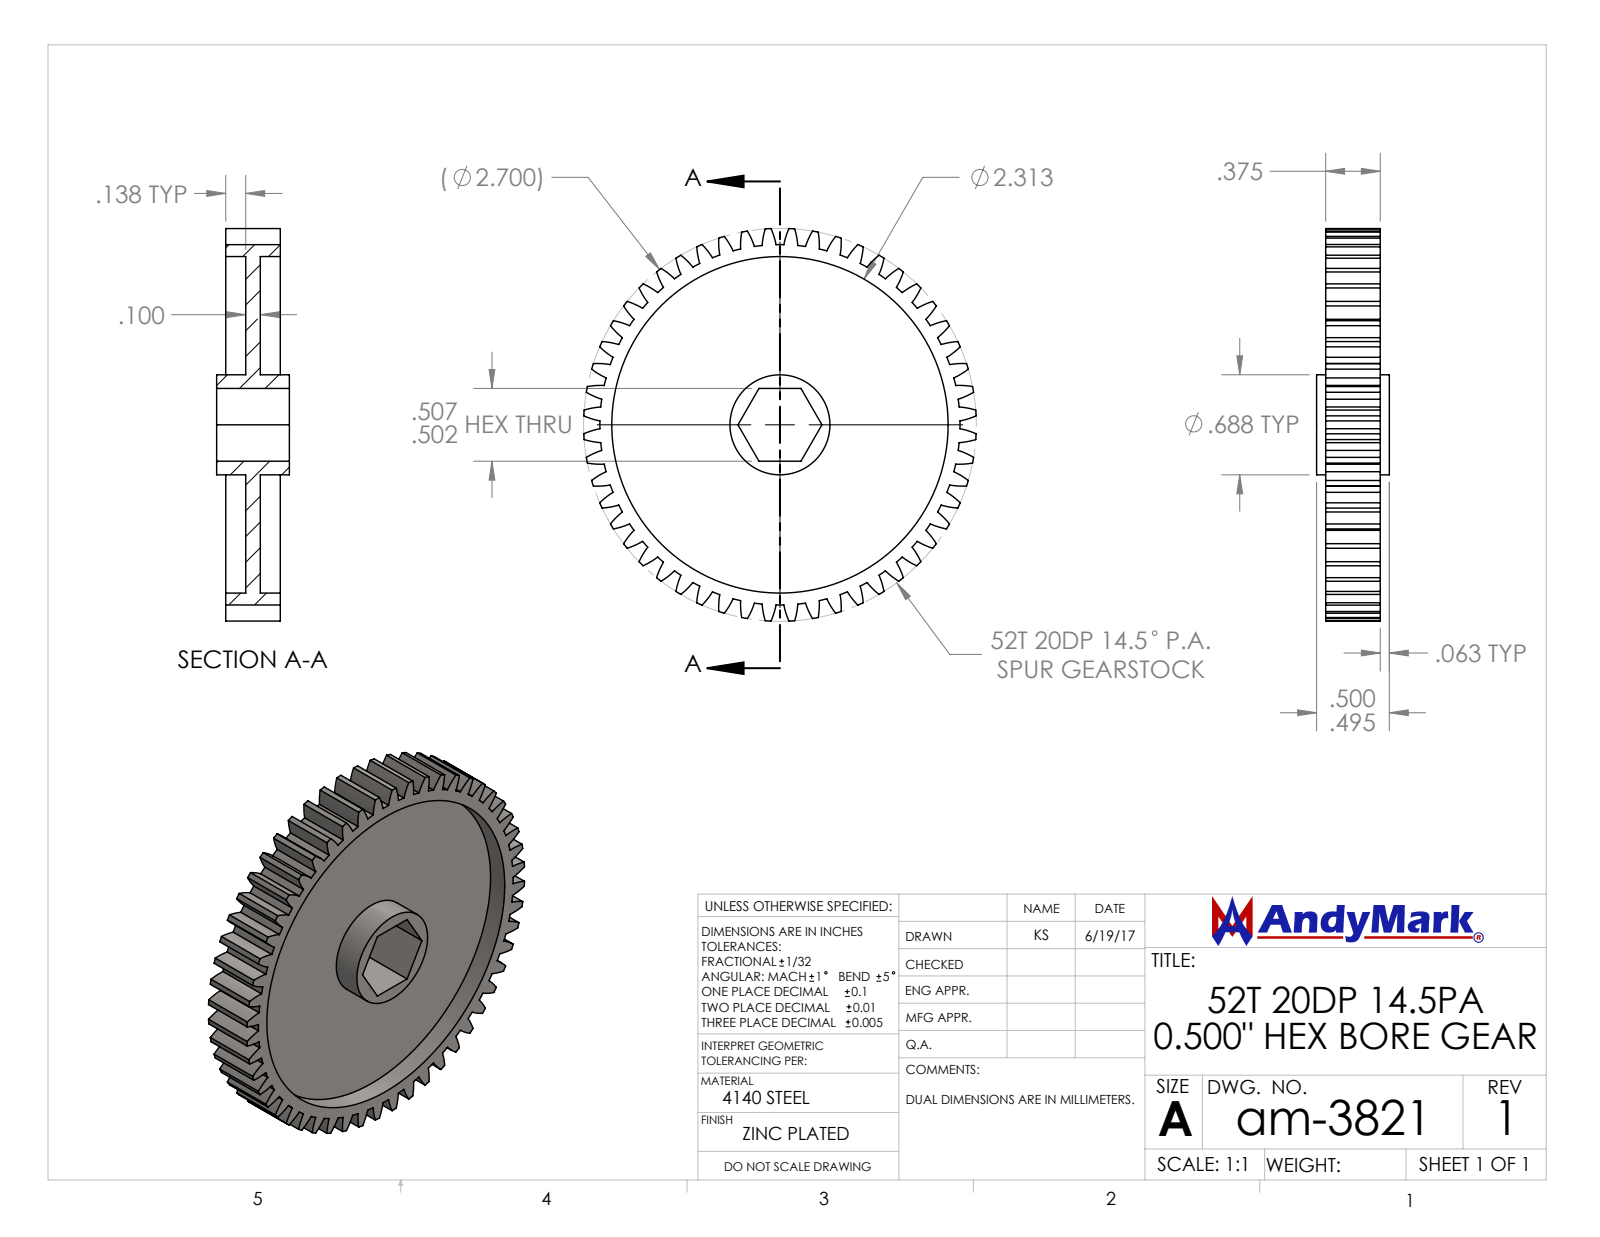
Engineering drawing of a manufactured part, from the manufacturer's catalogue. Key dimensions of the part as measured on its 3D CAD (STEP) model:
Part name (STEP PRODUCT): am-3821 52T 20DP 500hex 375 FW
STEP written by: SolidWorks 2019 (CONFIG_CONTROL_DESIGN)
Units: inches
Bodies: 1 solid, 337 faces (12 planar, 221 cylindrical, 104 other)
Overall size (bounding box): 2.697 × 2.697 × 0.5
Volume: 0.847 in³ · Surface area: 19.97 in²
Round holes (diameter × count): ⌀2.313 ×1
Round bosses / shafts (diameter × count): ⌀0.687 ×1
Partial cylindrical surfaces — rounded edges, fillets, slot ends (radius × count): R0.52 ×104, R1.238 ×1, R1.35 ×1
Main face-to-face distances: 0.1, 0.137, 0.237, 0.375, 0.238, 0.138, 0.5, 0.2, 0.3, 0.063
